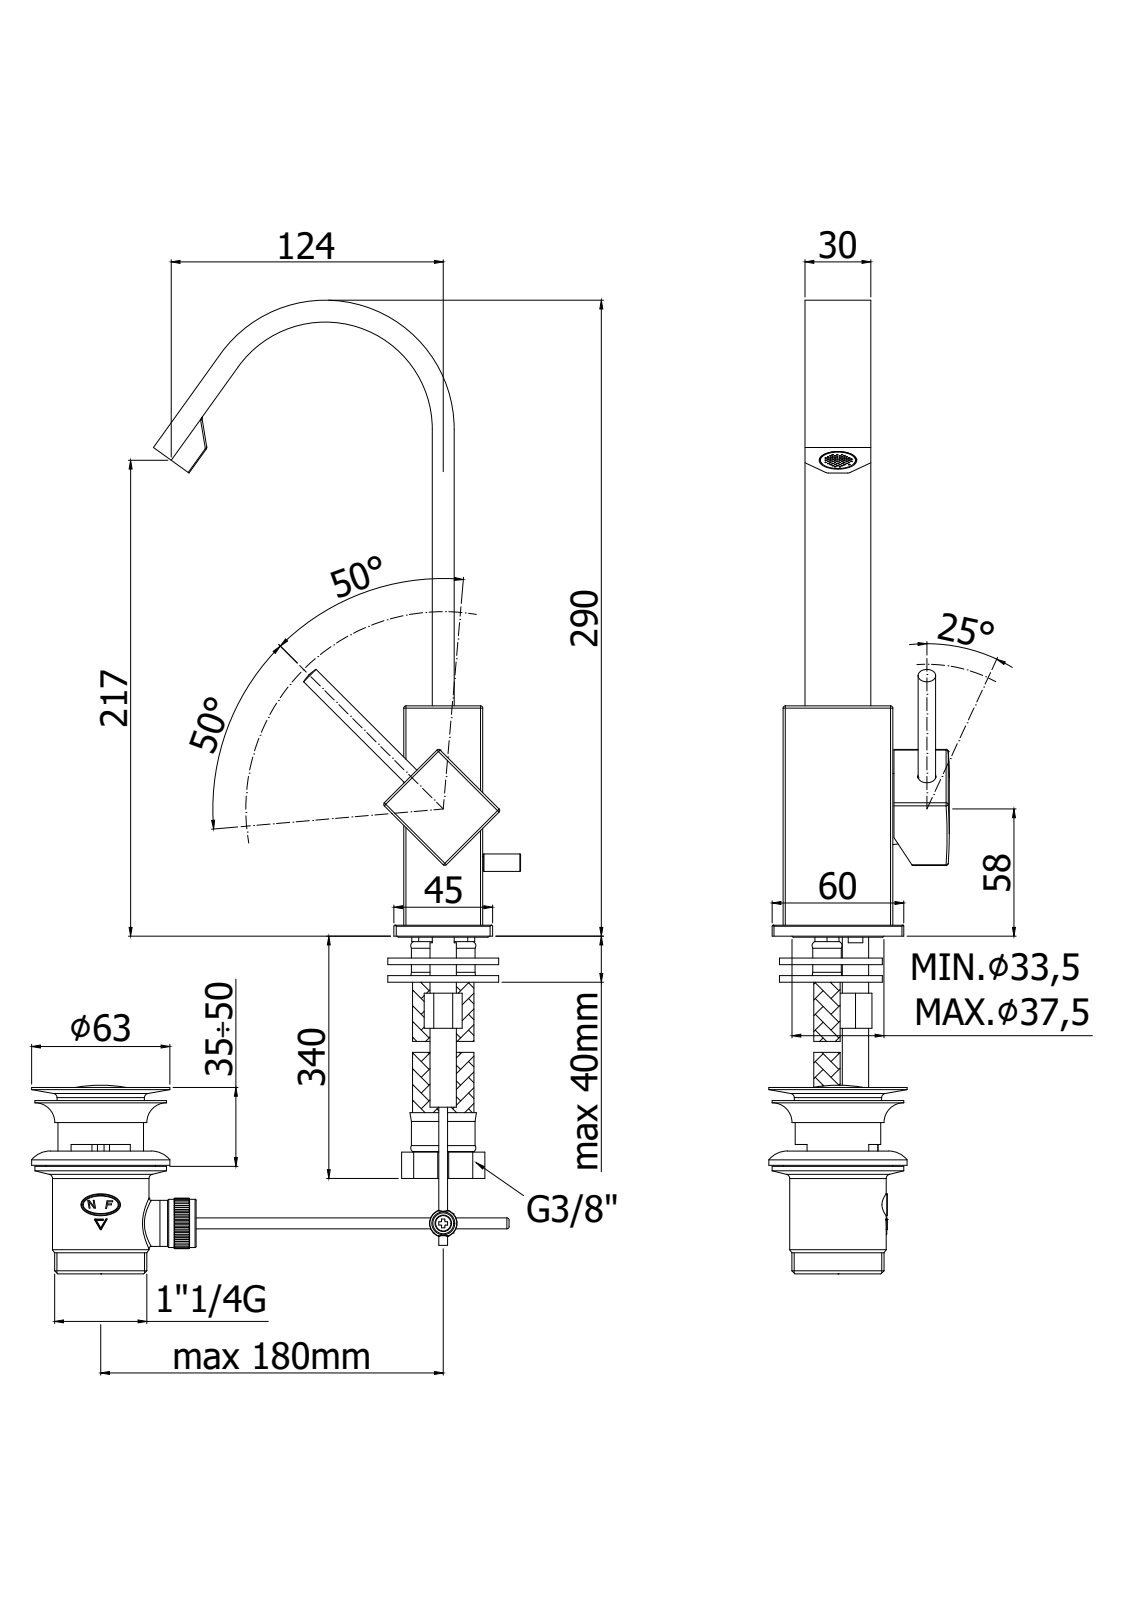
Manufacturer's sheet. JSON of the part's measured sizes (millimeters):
{"part_name": "LEA877CR", "step_written_by": "CREO PARAMETRIC BY PTC INC, 2020044 (CONFIG_CONTROL_DESIGN)", "units": "millimeters", "bodies": {"solids": 5, "faces": 3238, "planar": 2031, "cylindrical": 706, "other": 501}, "overall_size": [290.2, 160.93, 82.98], "volume_mm3": 234774, "surface_area_mm2": 111518, "round_holes": [[11, 4], [3.3, 3], [4.5, 3], [6, 3], [7, 3], [4.6, 2], [5, 2], [9, 2], [34, 2], [3, 1], [4, 1], [5.5, 1]], "round_bosses_or_shafts": [[0.9, 3], [20, 2], [12, 2], [10.8, 2], [8.2, 2], [4, 2], [38.8, 1], [32, 1]], "partial_cylinders_radius": [[0.5, 64], [0.12, 51], [1, 19], [0.6, 10], [0.7, 10], [0.8, 6], [0.65, 4], [0.85, 4]], "face_to_face_distances": [1.5, 10, 13, 8.5, 23, 21.5, 40, 14.5, 36, 7], "hole_center_spacings": [5.96, 6.72, 9.43, 10.12, 11.2, 11.31, 15.26, 18.07]}
